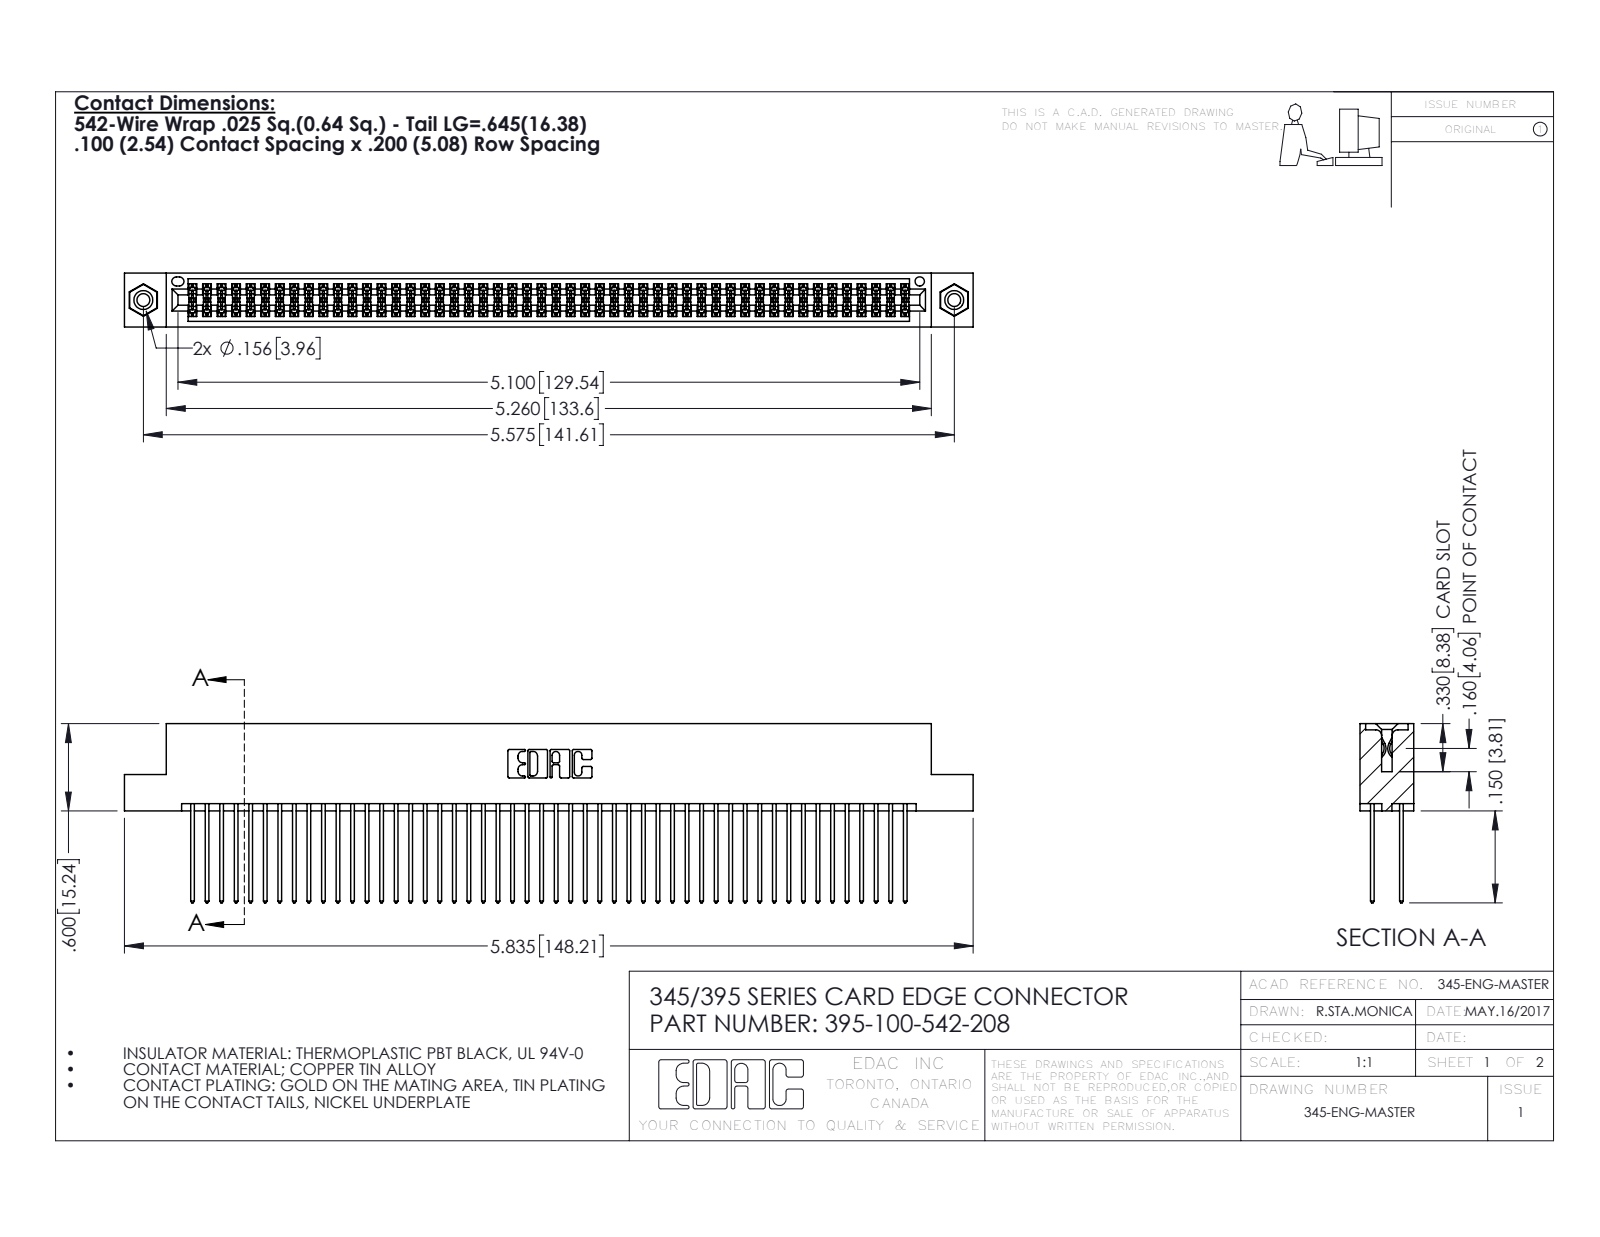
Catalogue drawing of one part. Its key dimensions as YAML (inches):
part_name: "345-292-001_345-293-142; 345-250-001_345-250-003-102; 345 Part_Flush Mounting Lugs - 0.156 Dia-TI; 395-100-542-208"
step_written_by: "SolidWorks 2016 (CONFIG_CONTROL_DESIGN)"
units: inches
bodies: {solids: 103, faces: 5186, planar: 3412, cylindrical: 1758, other: 16}
overall_size: [5.835, 1.232, 0.37]
volume: 0.911
surface_area: 37.85
round_holes:
  - {diameter: 0.089, count: 2}
  - {diameter: 0.125, count: 2}
  - {diameter: 0.156, count: 2}
  - {diameter: 0.064, count: 1}
round_bosses_or_shafts:
  - {diameter: 0.155, count: 2}
partial_cylinders:
  - {radius: 0.006, count: 150}
  - {radius: 0.01, count: 100}
  - {radius: 0.01, count: 22}
  - {radius: 0.007, count: 6}
  - {radius: 0.031, count: 6}
  - {radius: 0.026, count: 3}
  - {radius: 0.014, count: 2}
  - {radius: 0.019, count: 2}
face_to_face_distances: [0.072, 0.298, 0.2, 0.098, 0.272, 0.025, 0.225, 0.37, 0.175, 0.149]
hole_center_spacings: [0.27, 5.339, 5.575]
